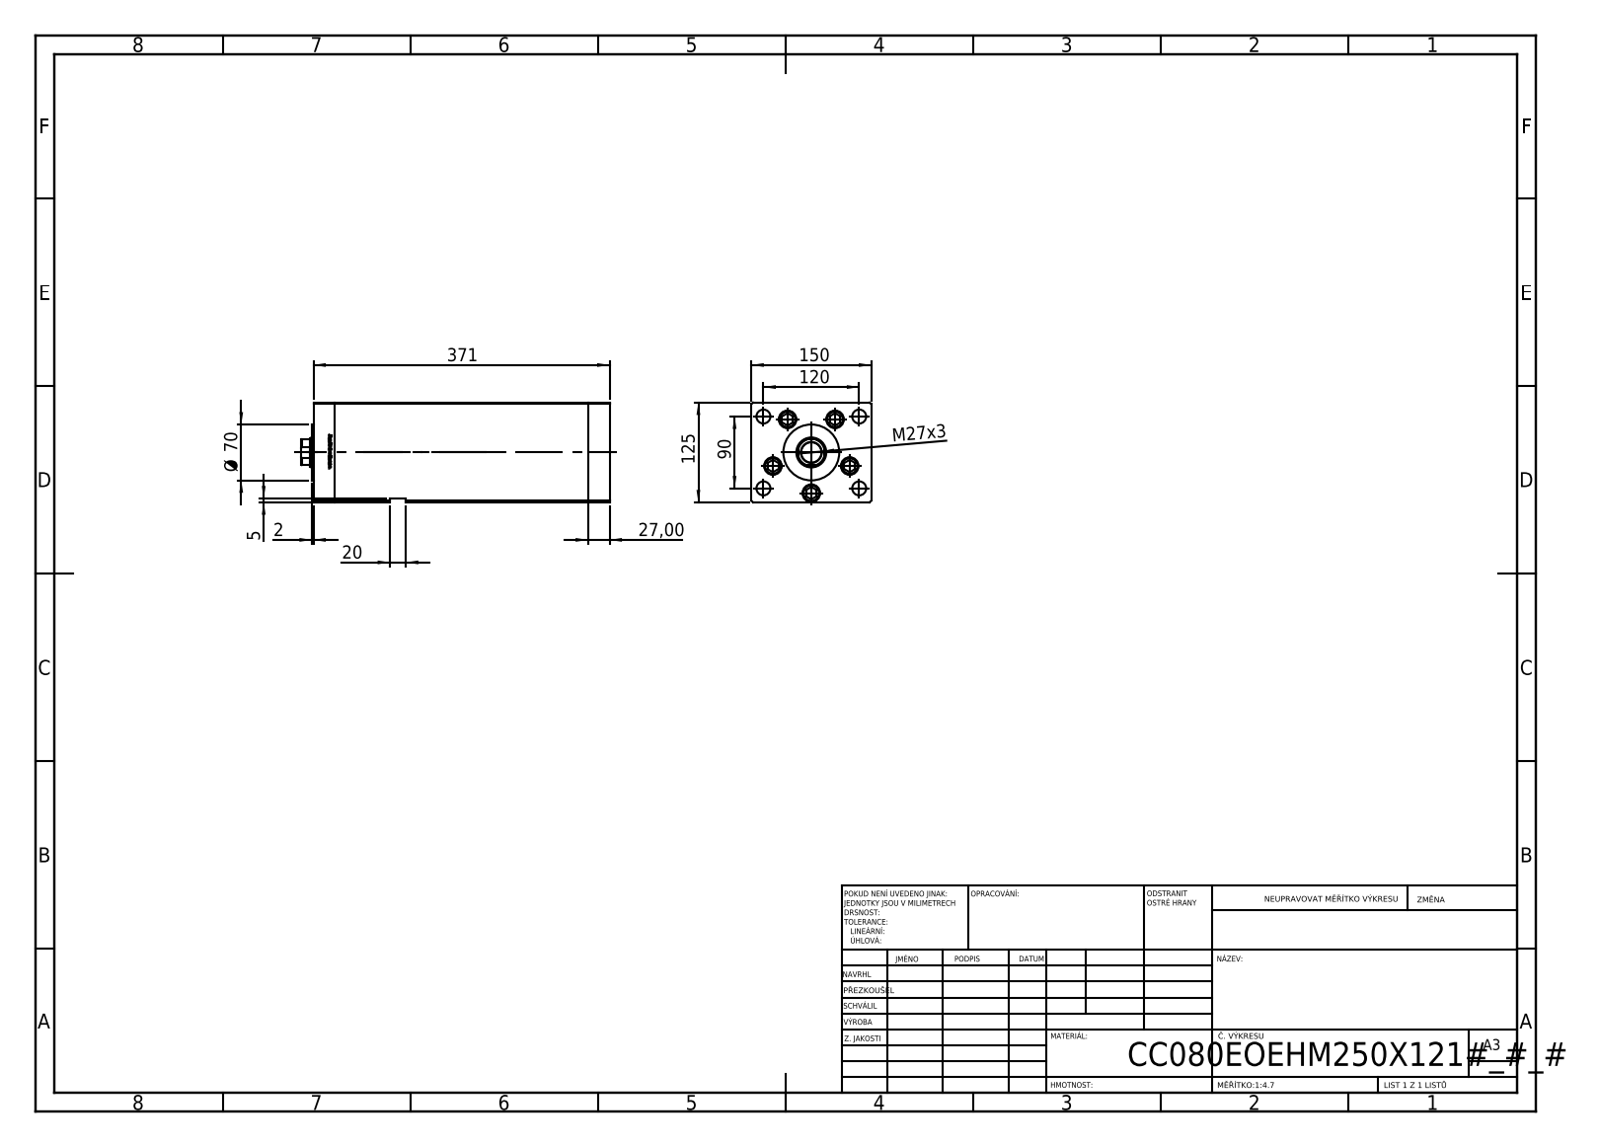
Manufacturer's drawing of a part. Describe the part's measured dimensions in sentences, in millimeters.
The part is named "V220C_FRONT_E; V220C_E MIDDLE; ALLEN BOLT; V220C_VC_E (+1 more)". Its 3-D file was written by "SolidWorks 2019 (CONFIG_CONTROL_DESIGN)". It is 14 solids with 1214 faces: 475 planar, 165 cylindrical and 574 other. Overall it measures 386 by 150 by 125 millimeters. Its volume is 5 602 000 cubic millimeters and its surface area 537 047 square millimeters. Round holes: 9 of diameter 17.5, 5 of diameter 22, 4 of diameter 17, 4 of diameter 23, 2 of diameter 2, 2 of diameter 13.16, 1 of diameter 25.5, 1 of diameter 36, 1 of diameter 37.5. Round bosses or shafts: 5 of diameter 21, 5 of diameter 8, 1 of diameter 80, 1 of diameter 70. Partial cylindrical surfaces (rounded edges, fillets, slot ends): 2 of radius 0.93, 1 of radius 17.5. The main face-to-face distances are 125, 150, 27, 344, 317, 33.5, 6.5, 371, 310.5, 337.5. The hole center spacings are 51, 75, 30.43, 30.48, 58.89, 60.3, 61.25, 63.14.
